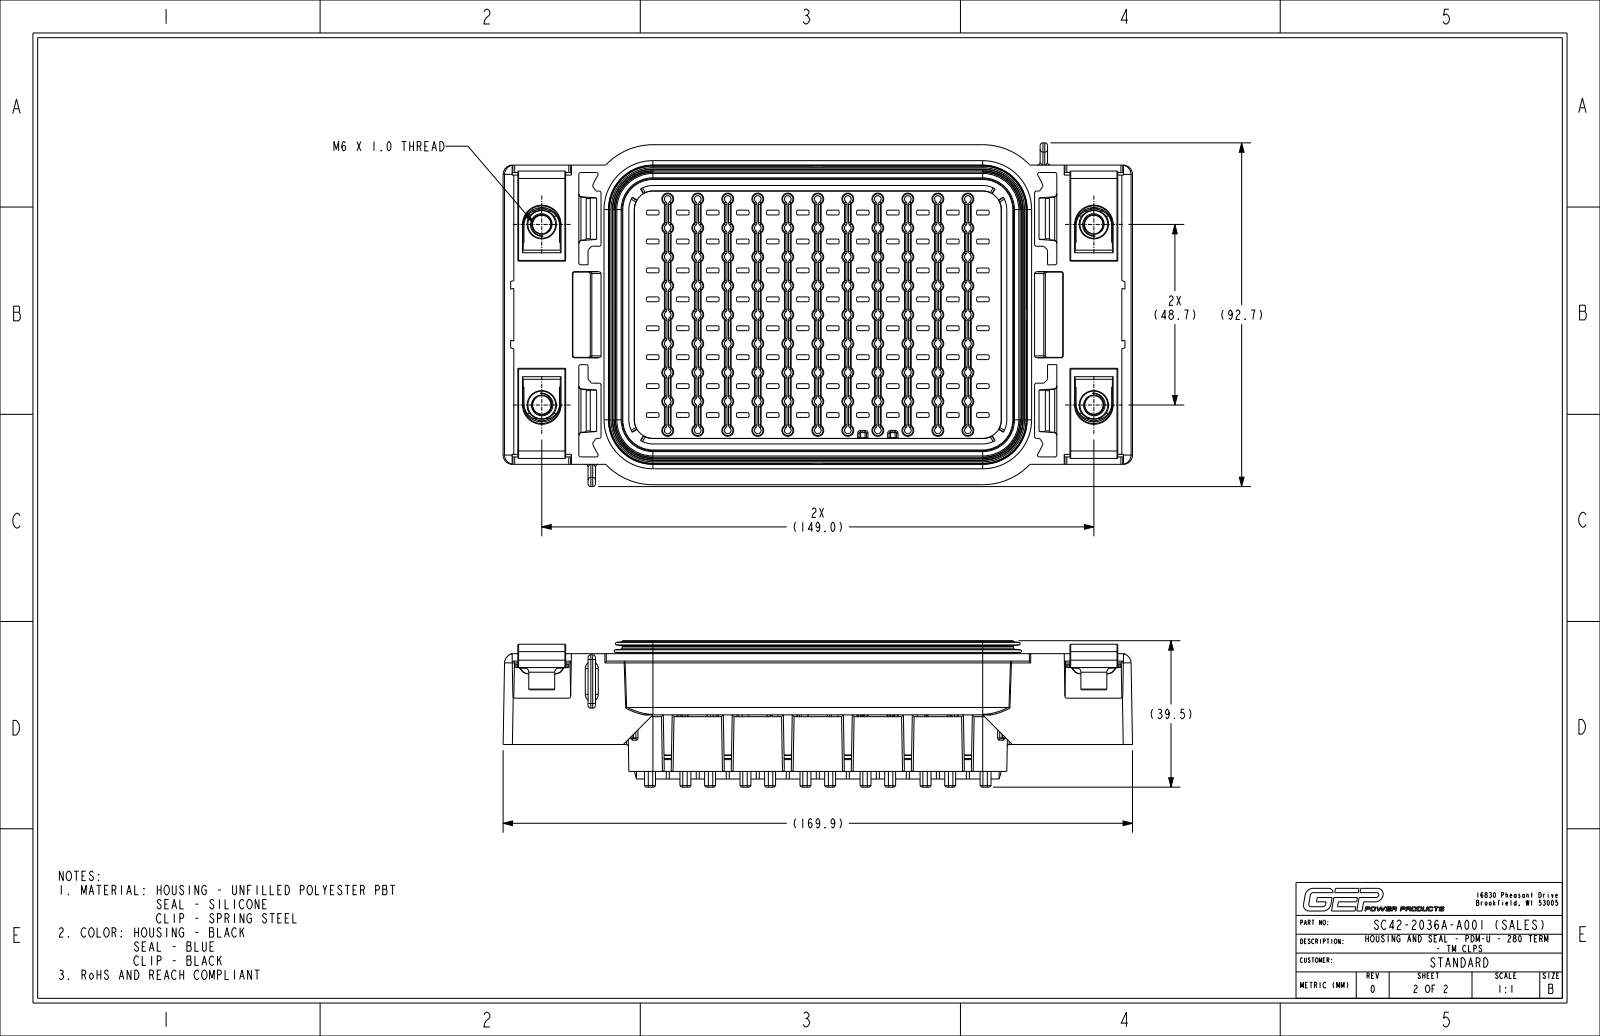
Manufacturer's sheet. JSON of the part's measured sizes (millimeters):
{"part_name": "SC42-2036A-A001_NCF_SW0001", "step_written_by": "CREO PARAMETRIC BY PTC INC, 2024014 (CONFIG_CONTROL_DESIGN)", "units": "millimeters", "bodies": {"solids": 5, "faces": 9532, "planar": 2301, "cylindrical": 2966, "other": 4265}, "overall_size": [169.85, 92.7, 39.5], "volume_mm3": 228451, "surface_area_mm2": 149631, "round_holes": [[6.7, 96], [3.18, 8], [5, 4], [7.5, 4], [10.5, 4]], "round_bosses_or_shafts": [[7, 4], [6, 1]], "partial_cylinders_radius": [[0.5, 994], [0.4, 411], [1.4, 99], [4.45, 96], [0.2, 92], [0.3, 56], [0.75, 24], [2.9, 21]], "face_to_face_distances": [5, 28.8, 9, 2, 7, 23.8, 16.2, 3, 15, 26.8], "hole_center_spacings": [8.1, 16.2, 17.58, 55.2, 56.95, 15.6, 24.3, 25.52]}
